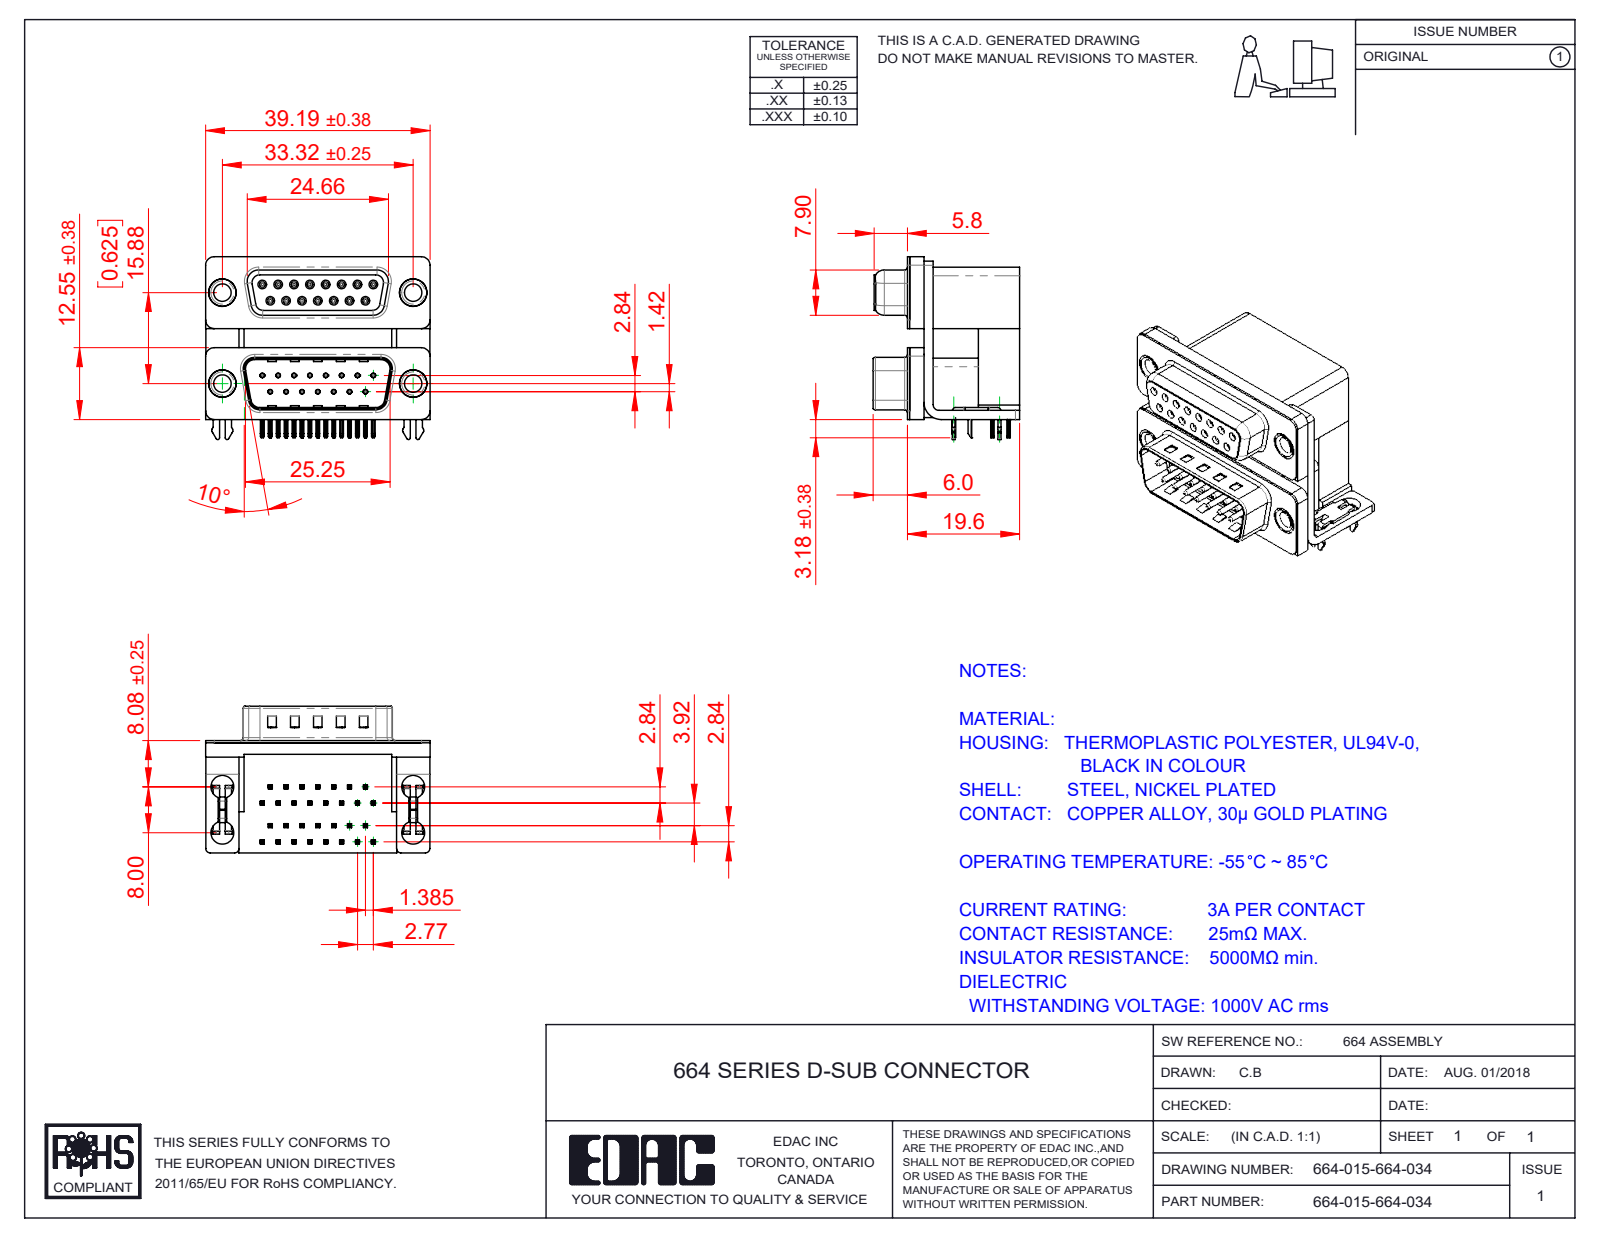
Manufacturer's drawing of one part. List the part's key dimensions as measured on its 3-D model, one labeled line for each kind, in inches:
Part name (STEP PRODUCT): 664 Housing Lower_15 Contacts; 664 Housing Spacer_15 Contacts L; 664 Thru Hole Rivet; 664 Contact Top Upper_L (+8 more)
STEP written by: SolidWorks 2020 (CONFIG_CONTROL_DESIGN)
Units: inches
Bodies: 43 solids, 3980 faces (2117 planar, 1028 cylindrical, 835 other)
Overall size (bounding box): 1.543 × 1.257 × 1.008
Volume: 0.886 in³ · Surface area: 25.51 in²
Round holes (diameter × count): ⌀0.031 ×30, ⌀0.014 ×15, ⌀0.035 ×15, ⌀0.157 ×8, ⌀0.12 ×4, ⌀0.138 ×4, ⌀0.189 ×4, ⌀0.197 ×4
Round bosses / shafts (diameter × count): ⌀0.047 ×15, ⌀0.03 ×15, ⌀0.193 ×4, ⌀0.187 ×4, ⌀0.152 ×4
Partial cylindrical surfaces — rounded edges, fillets, slot ends (radius × count): R0.004 ×122, R0.01 ×70, R0.006 ×60, R0.005 ×30, R0.014 ×30, R0.02 ×16, R0.059 ×16, R0.013 ×15
Main face-to-face distances: 0.016, 0.756, 0.657, 0.098, 0.283, 0.472, 0.374, 0.086, 0.421, 0.114
Hole centre spacings: 0.124, 0.109, 0.635, 0.218, 0.662, 0.327, 0.625, 0.706
